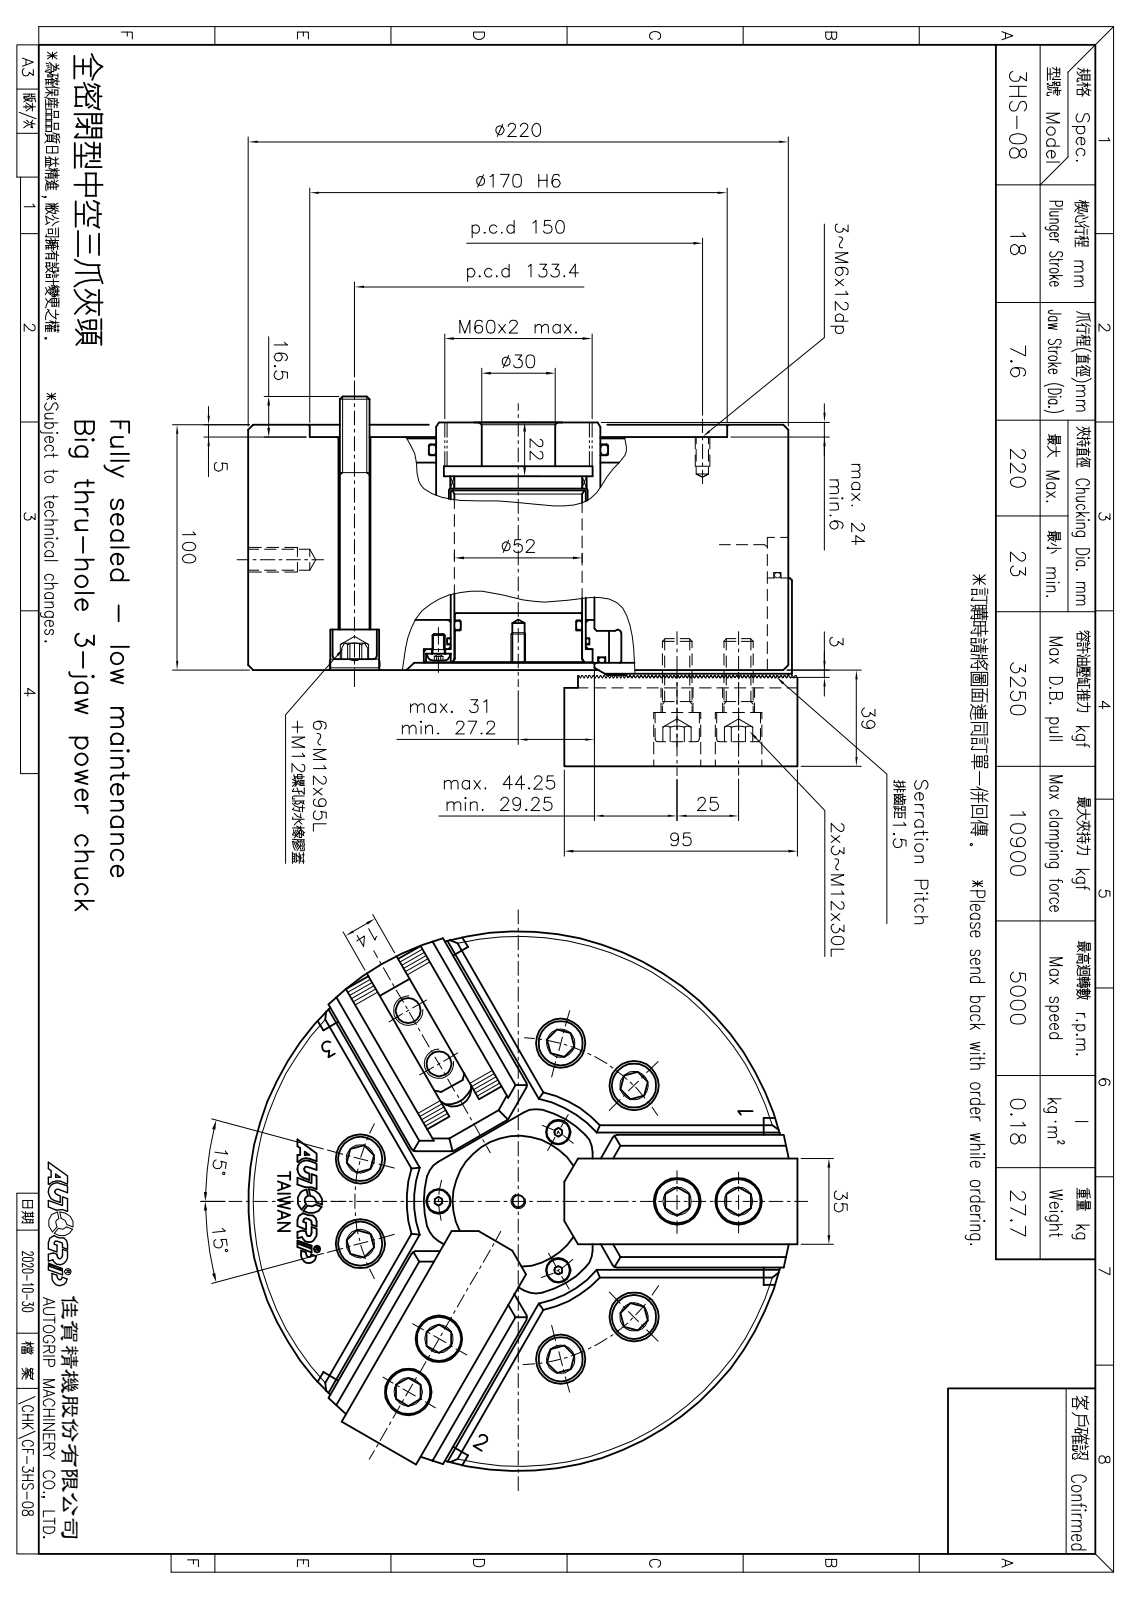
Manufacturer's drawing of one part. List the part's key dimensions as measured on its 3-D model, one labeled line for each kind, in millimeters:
Part name (STEP PRODUCT): 3PS-08-09000; CF-3HS-08-07000; CF-3H-208-04000(T型塊); CF-3HS-08-08000 (+8 more)
STEP written by: SolidWorks 2020 (CONFIG_CONTROL_DESIGN)
Units: millimetres
Bodies: 32 solids, 2988 faces (2060 planar, 755 cylindrical, 173 other)
Overall size (bounding box): 223.75 × 220 × 150.75
Volume: 3 927 000 mm³ · Surface area: 513 939 mm²
Round holes (diameter × count): ⌀4 ×6, ⌀10.2 ×6, ⌀13.5 ×6, ⌀20 ×6, ⌀5 ×4, ⌀13 ×4, ⌀19 ×4, ⌀8.5 ×1, ⌀52 ×1, ⌀52.2 ×1, ⌀55 ×1, ⌀55.2 ×1
Round bosses / shafts (diameter × count): ⌀18 ×10, ⌀12 ×10, ⌀20.5 ×6, ⌀10.5 ×6, ⌀220 ×1, ⌀77 ×1, ⌀73 ×1, ⌀67 ×1
Partial cylindrical surfaces — rounded edges, fillets, slot ends (radius × count): R0.1 ×263, R2 ×12, R20 ×10, R7.3 ×6, R10 ×6, R110 ×3
Main face-to-face distances: 47, 95, 50, 10, 11.5, 5, 1, 35.5, 35, 21.5
Hole centre spacings: 115.53, 25, 79.16, 1.5, 63.55, 66.7, 80.04, 95.87
